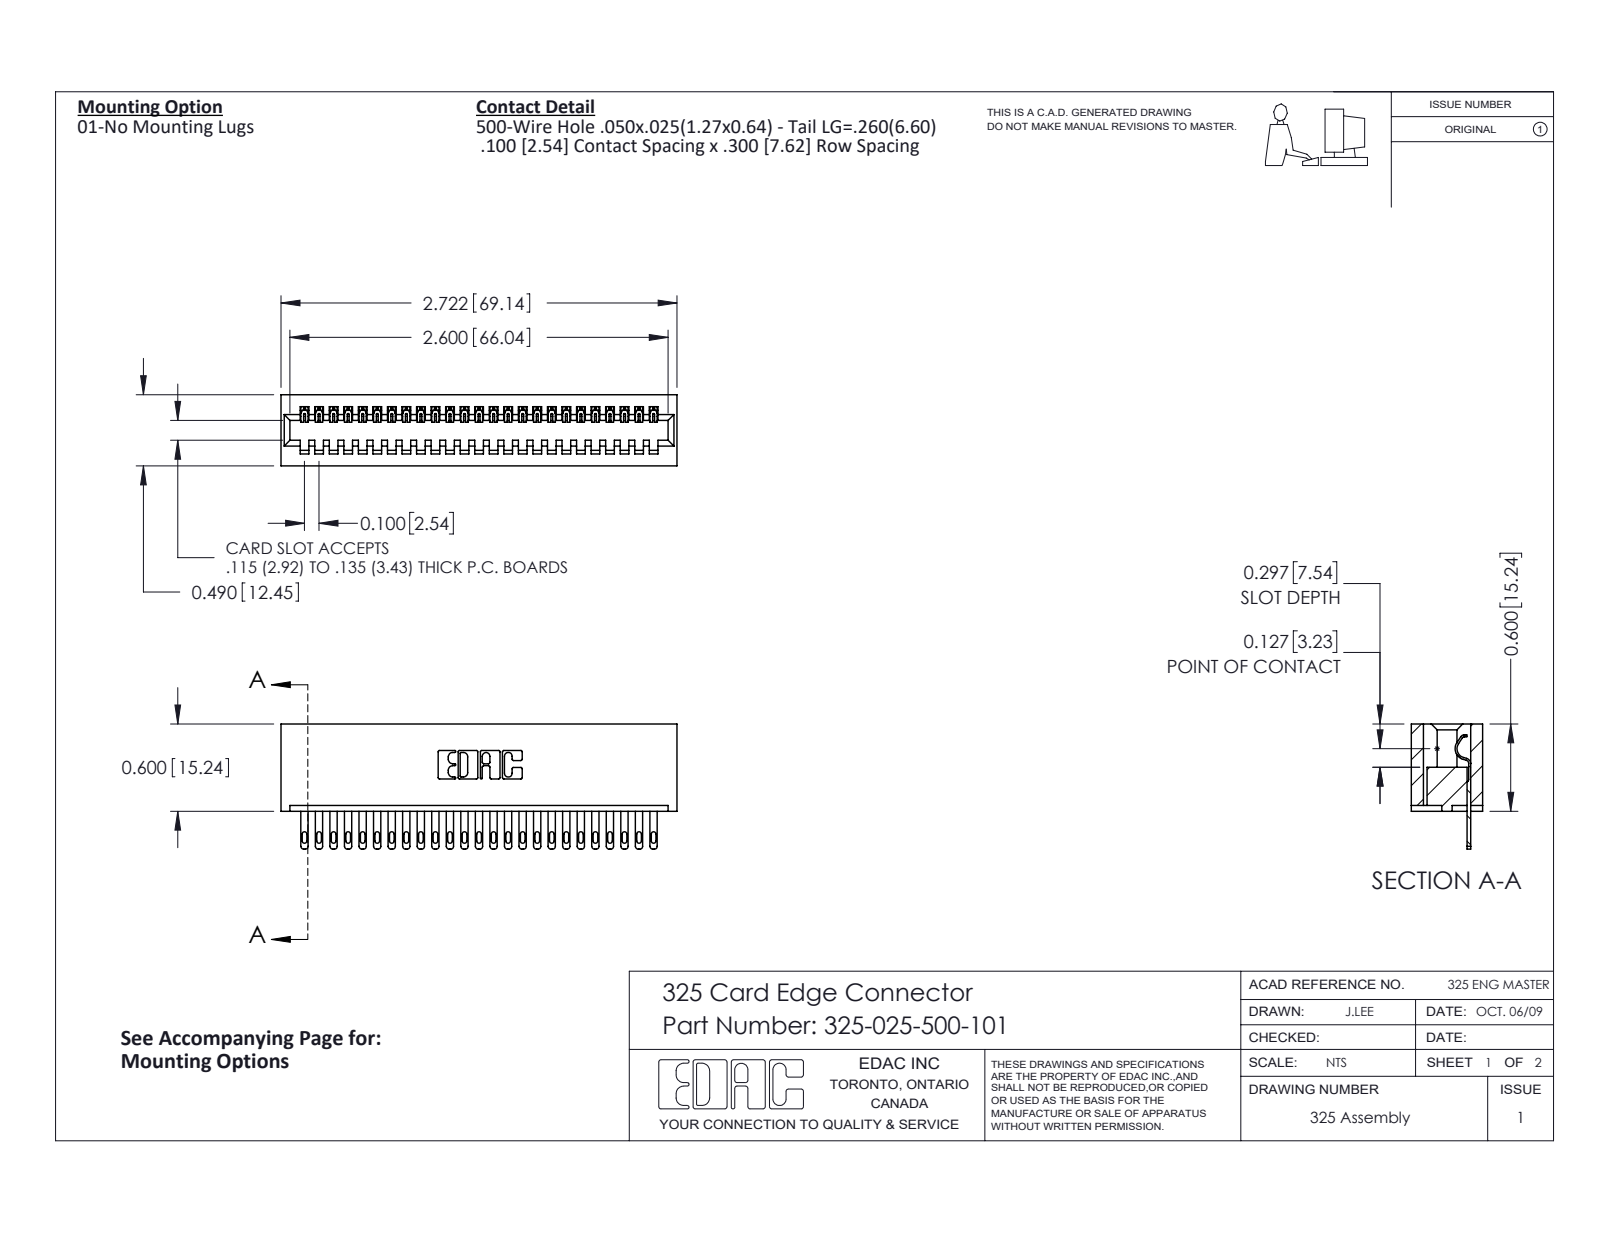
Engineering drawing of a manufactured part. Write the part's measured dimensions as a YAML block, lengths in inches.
part_name: "325-292-001_325-293-100; 325 Part_Lugless; 325-025-500-101"
step_written_by: "SolidWorks 2016 (CONFIG_CONTROL_DESIGN)"
units: inches
bodies: {solids: 26, faces: 1456, planar: 966, cylindrical: 490, other: 0}
overall_size: [2.722, 0.86, 0.49]
volume: 0.563
surface_area: 16.03
partial_cylinders:
  - {radius: 0.006, count: 50}
  - {radius: 0.016, count: 50}
  - {radius: 0.02, count: 50}
  - {radius: 0.01, count: 22}
  - {radius: 0.007, count: 6}
  - {radius: 0.031, count: 6}
  - {radius: 0.026, count: 3}
  - {radius: 0.014, count: 1}
face_to_face_distances: [0.083, 0.407, 0.3, 0.49, 0.107, 0.383, 0.025, 0.325, 0.1, 0.56]
